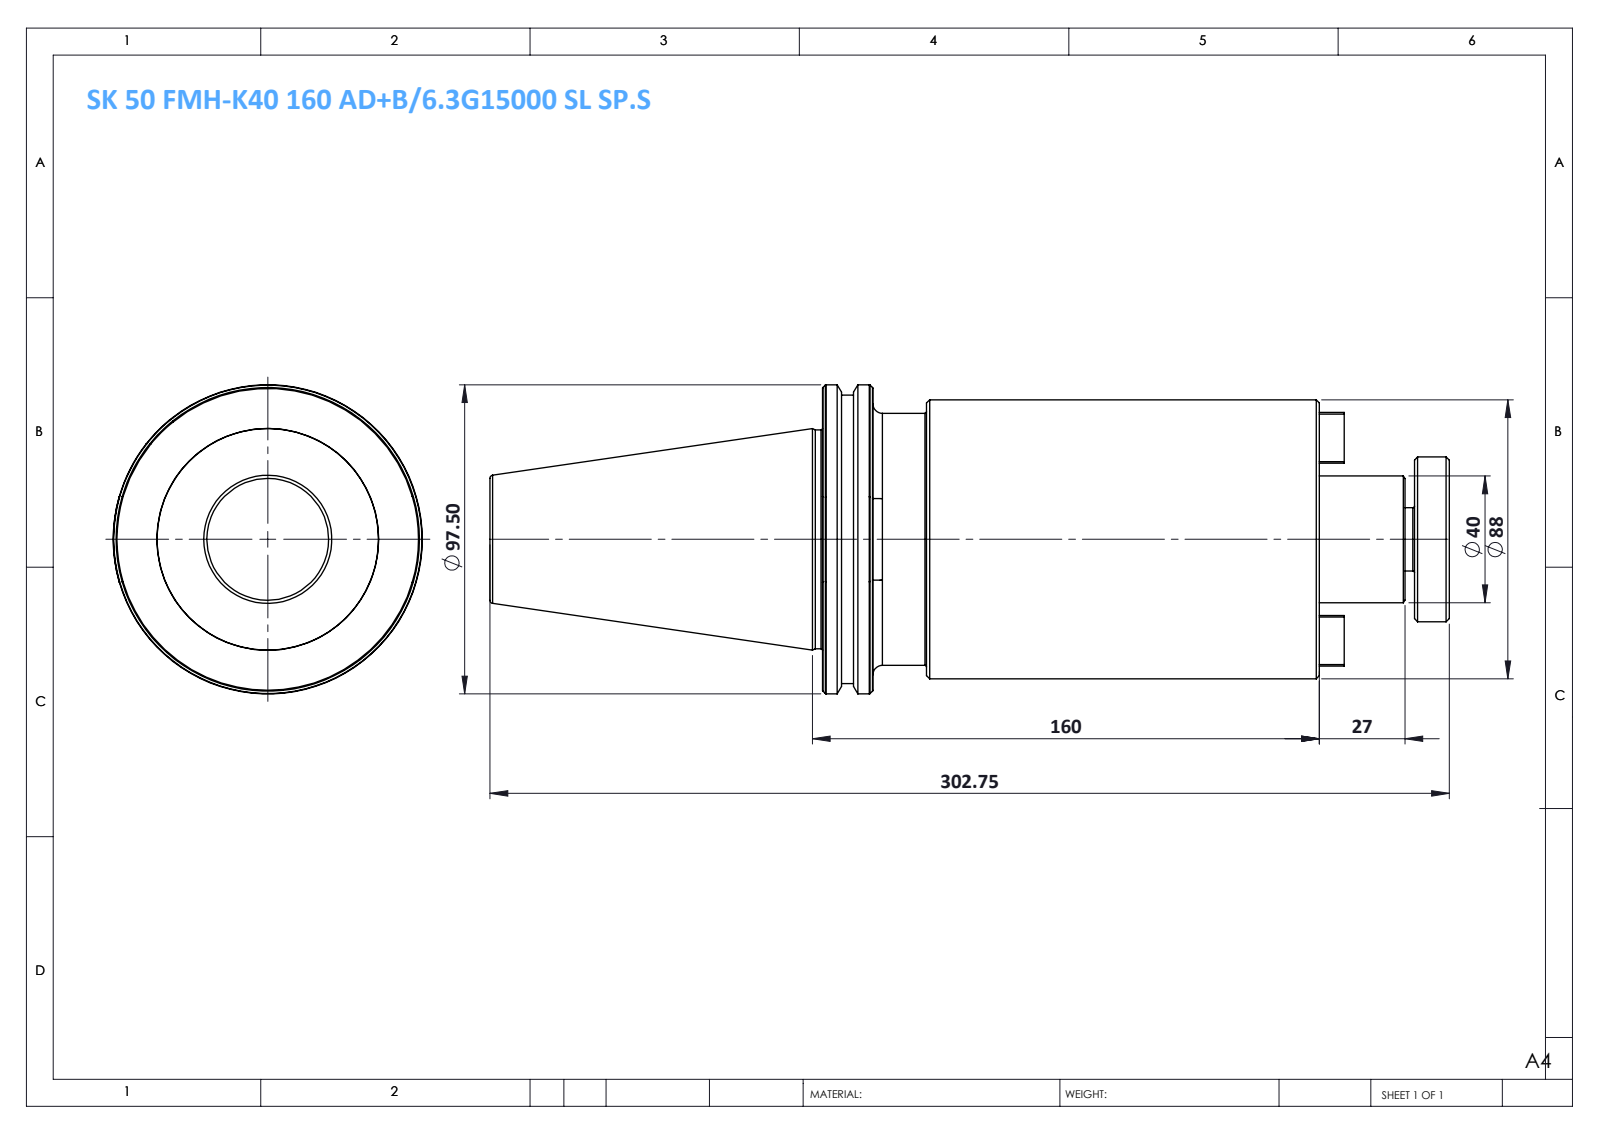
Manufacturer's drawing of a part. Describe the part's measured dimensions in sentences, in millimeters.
The part is named "SK50 FMH40 160 AD-6.3G15000 SL SP.S". Its 3-D file was written by "SolidWorks 2014 (CONFIG_CONTROL_DESIGN)". It is 1 solid with 110 faces: 28 planar, 18 cylindrical and 64 other. Overall it measures 302.75 by 97.5 by 97.5 millimeters. Its volume is 1 274 000 cubic millimeters and its surface area 86 355 square millimeters. Round bosses or shafts: 1 of diameter 97.5, 1 of diameter 91, 1 of diameter 88, 1 of diameter 79.5, 1 of diameter 69, 1 of diameter 52, 1 of diameter 40, 1 of diameter 20. The main face-to-face distances are 156.8, 41, 197.8, 11, 30, 186.8, 181.9, 170.9, 140.9, 15.9.
